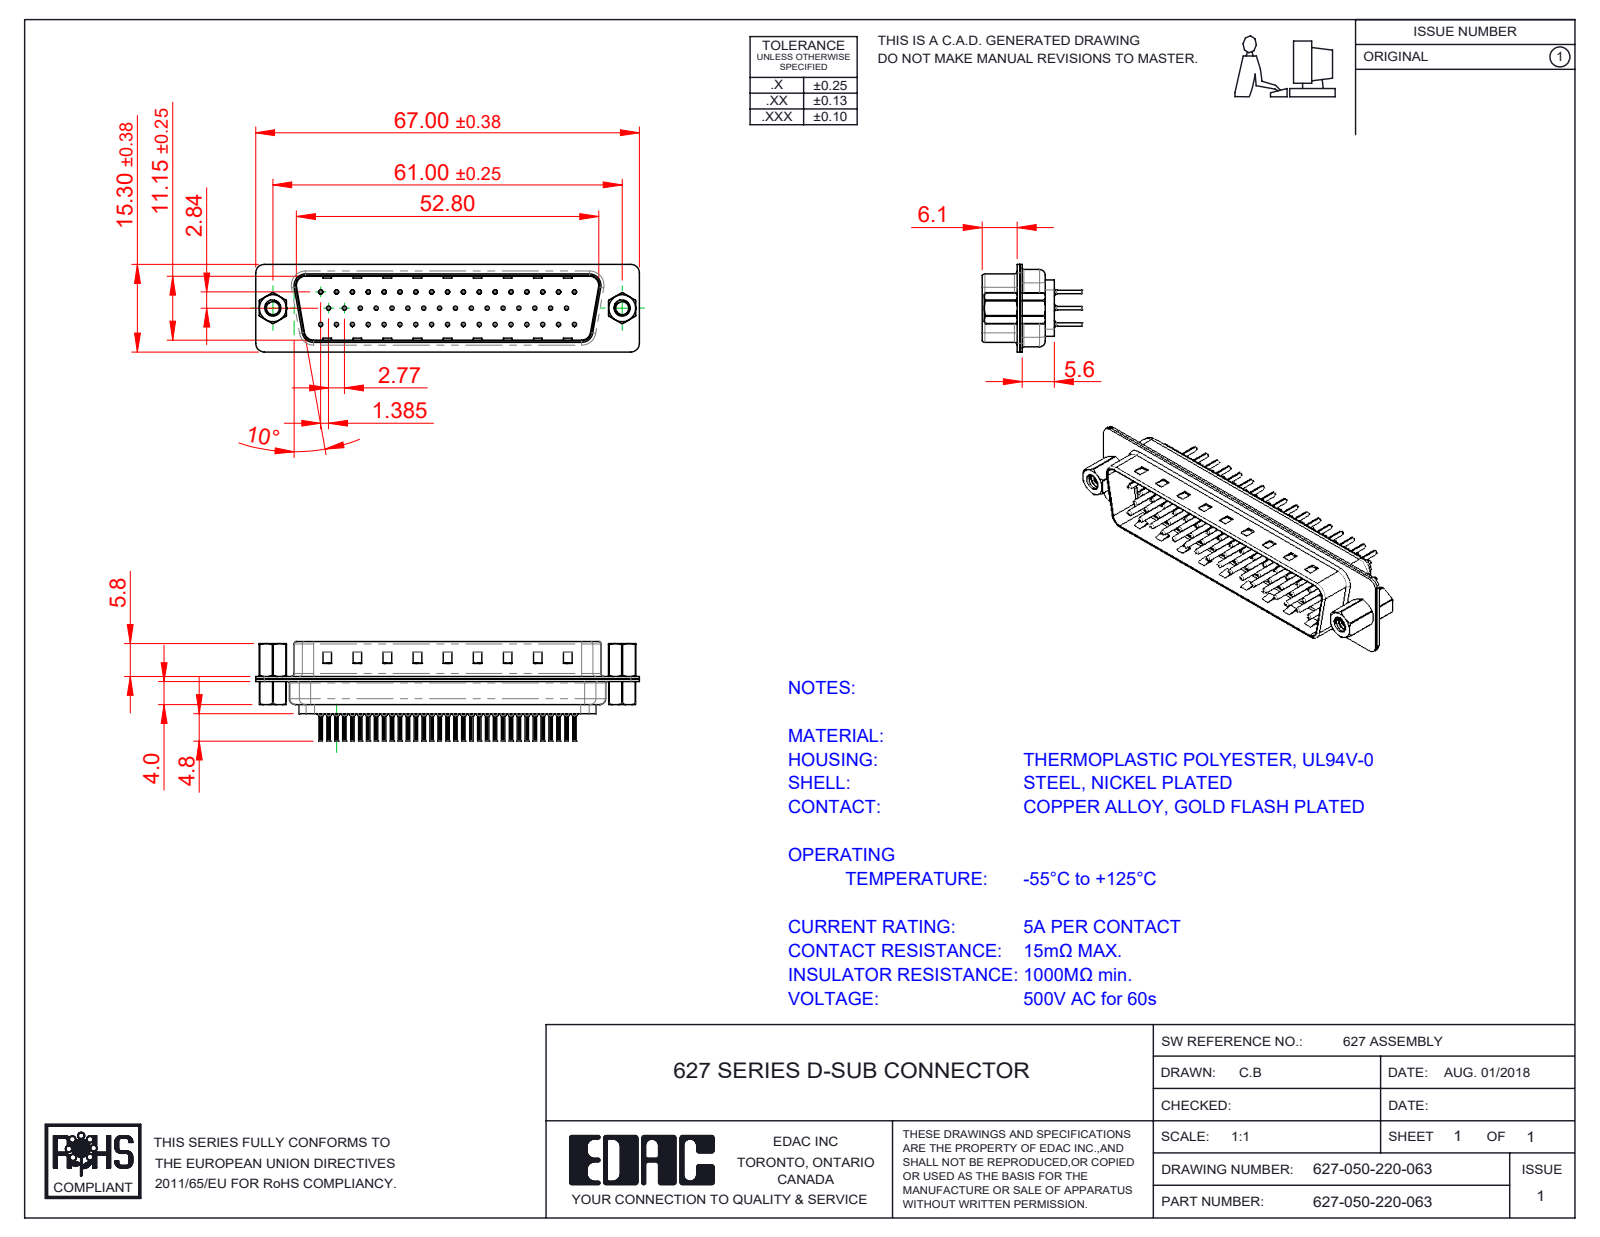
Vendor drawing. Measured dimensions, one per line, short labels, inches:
name: 627-050-220-063; 627 4-40 Hex Standoff; 627 Shell Rear_50 Contacts; 627 Contact Row 2_20L (+5 more)
written by: SolidWorks 2020 (CONFIG_CONTROL_DESIGN)
unit: in
bodies: 57 solids, 5434 faces (1425 planar, 2061 cylindrical, 1948 other)
size: 2.638 × 0.681 × 0.602
volume: 0.283 in³; area: 20.24 in²
holes: 50× ⌀0.008, 50× ⌀0.014, 50× ⌀0.043, 50× ⌀0.063, 2× ⌀0.089, 2× ⌀0.09, 2× ⌀0.157, 2× ⌀0.189
bosses: 50× ⌀0.079, 50× ⌀0.059, 50× ⌀0.03, 50× ⌀0.024, 2× ⌀0.197, 2× ⌀0.193, 2× ⌀0.11
rounds: 100× R0.004, 16× R0.059, 12× R0.079, 8× R0.02, 8× R0.063, 4× R0.01, 4× R0.024, 4× R0.026
face distances: 0.016, 0.018, 0.455, 0.035, 0.238, 0.256, 0.031, 0.485, 0.077, 0.03
hole spacings: 0.124, 0.109, 0.218, 0.327, 0.436, 0.545, 0.654, 0.198
